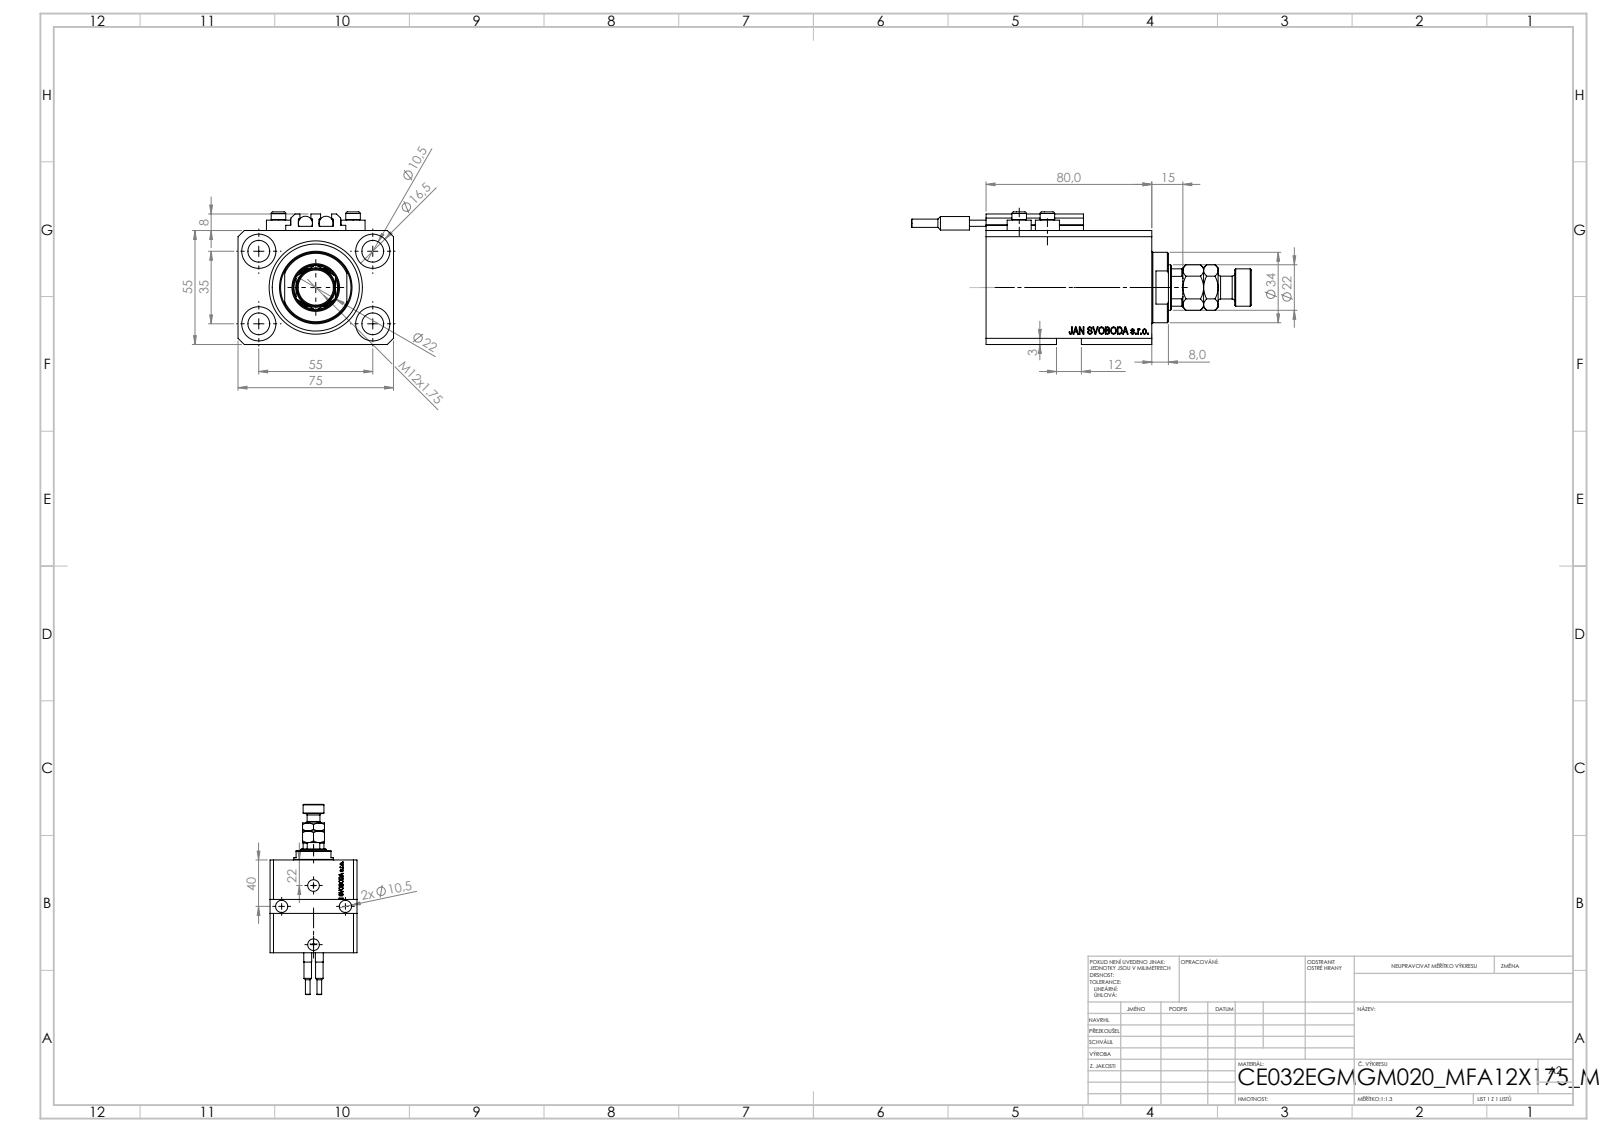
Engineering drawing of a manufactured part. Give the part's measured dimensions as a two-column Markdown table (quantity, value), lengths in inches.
| quantity | value |
| --- | --- |
| part name | ALLEN BOLT V250CE; SWITCH_V250CE; V250CE_C_VCP; V250CE_VC_E (+2 more) |
| STEP written by | SolidWorks 2019 (CONFIG_CONTROL_DESIGN) |
| units | inches |
| bodies | 11 solids, 1168 faces (562 planar, 142 cylindrical, 464 other) |
| overall size | 6.457 × 2.953 × 2.52 |
| volume | 18.03 in³ |
| surface area | 123.9 in² |
| round holes (diameter × count) | 0.413 × 7, 0.049 × 4, 0.157 × 4, 0.65 × 4, 0.394 × 2, 0.518 × 2, 0.787 × 2, 0.866 × 1, 1.26 × 1, 1.772 × 1 |
| round bosses / shafts (diameter × count) | 0.457 × 4, 0.276 × 4, 0.268 × 2, 0.256 × 2, 0.157 × 2, 1.339 × 1, 0.709 × 1, 0.433 × 1 |
| partial cylindrical surfaces (radius × count) | 0.008 × 10, 0.413 × 1 |
| main face-to-face distances | 2.165, 2.953, 0.591, 3.15, 0.118, 2.559, 2.169, 0.39, 2.244, 2.76 |
| hole center spacings | 1.283, 2.165, 0.535, 0.555, 0.783, 0.792, 1.016, 1.121 |
